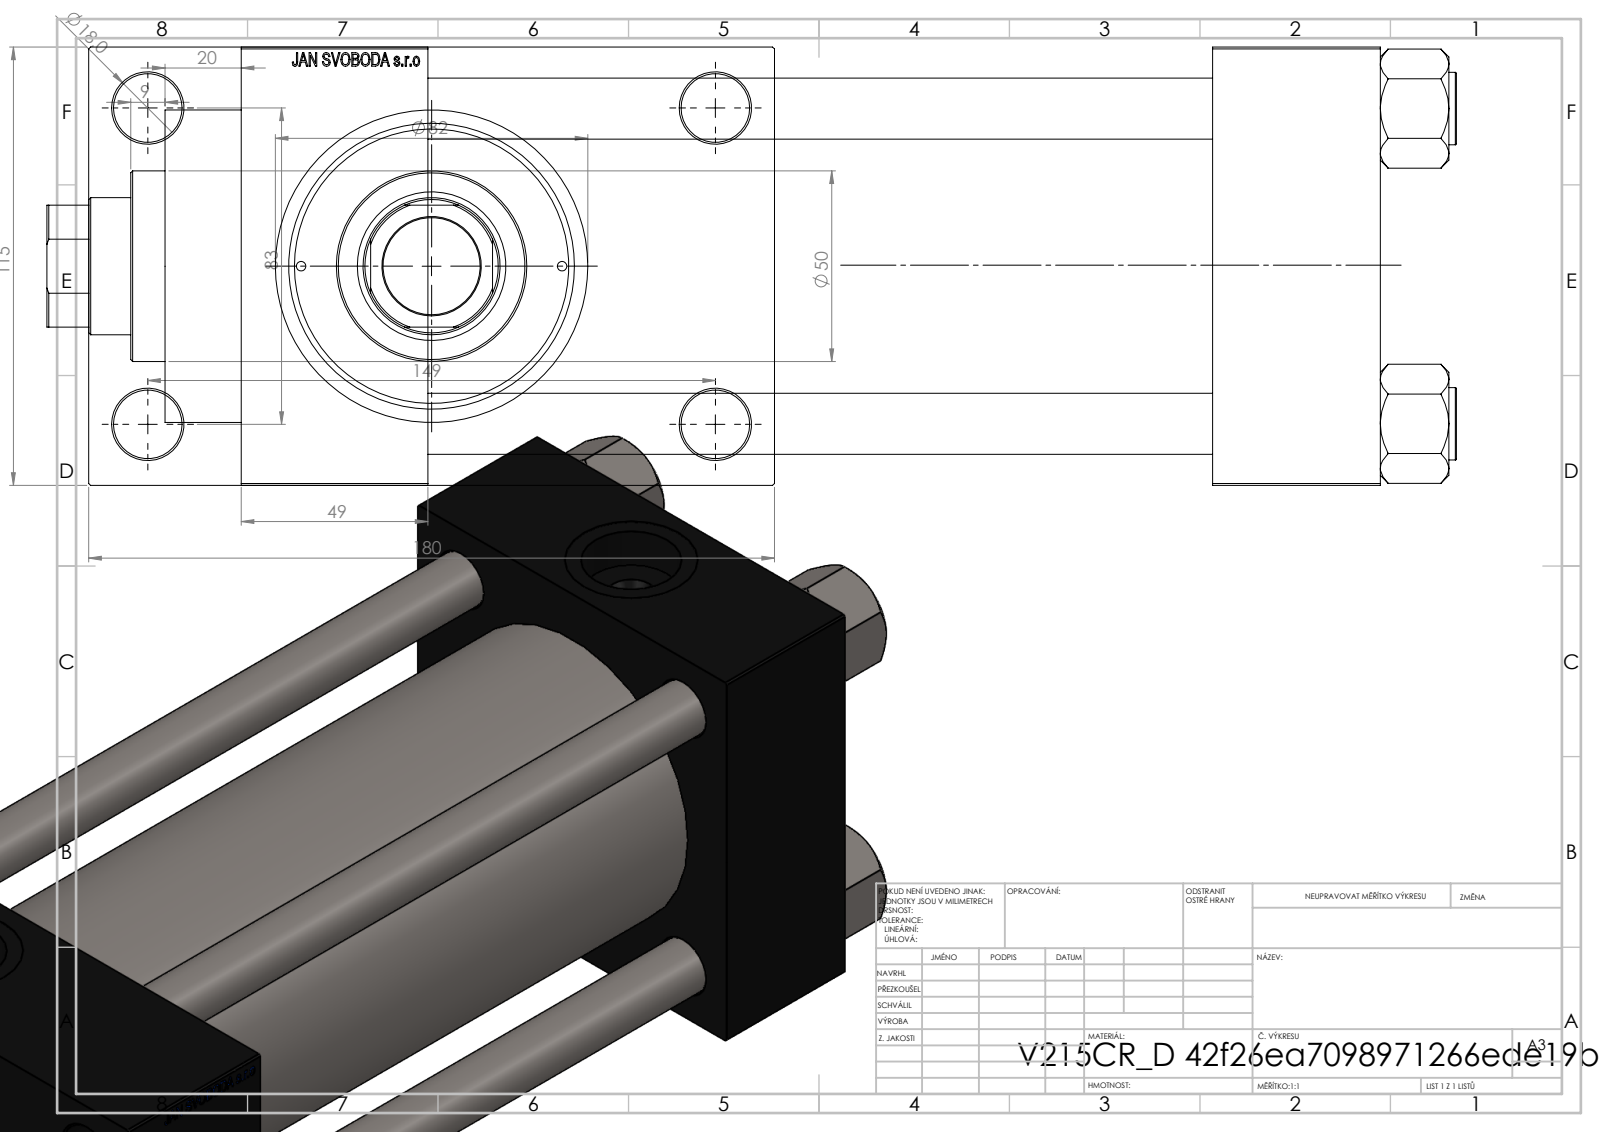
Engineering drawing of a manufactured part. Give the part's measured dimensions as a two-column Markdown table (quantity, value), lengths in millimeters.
| quantity | value |
| --- | --- |
| part name | V215CR_D_TYCINKA; V215_VC_A; V215CR_VCP_D; NUT_M5_D (+1 more) |
| STEP written by | SolidWorks 2019 (CONFIG_CONTROL_DESIGN) |
| units | millimeters |
| bodies | 11 solids, 1160 faces (547 planar, 93 cylindrical, 520 other) |
| overall size | 370 × 180 × 115 |
| volume | 2 361 000 mm³ |
| surface area | 410 779 mm² |
| round holes (diameter × count) | 16 × 4, 18 × 4, 2.5 × 2, 7 × 2, 26.44 × 2, 35 × 2, 25.5 × 1, 36 × 1, 39 × 1, 61 × 1, 72 × 1, 80 × 1 |
| round bosses / shafts (diameter × count) | 19 × 4, 86 × 1, 82 × 1, 50 × 1 |
| partial cylindrical surfaces (radius × count) | 17.5 × 1 |
| main face-to-face distances | 115, 206, 255, 49, 44, 250, 299, 32.5, 147.5, 180 |
| hole center spacings | 33.15, 41.96, 57.81, 58.48, 82.7, 85.28, 86.17, 89.24 |
